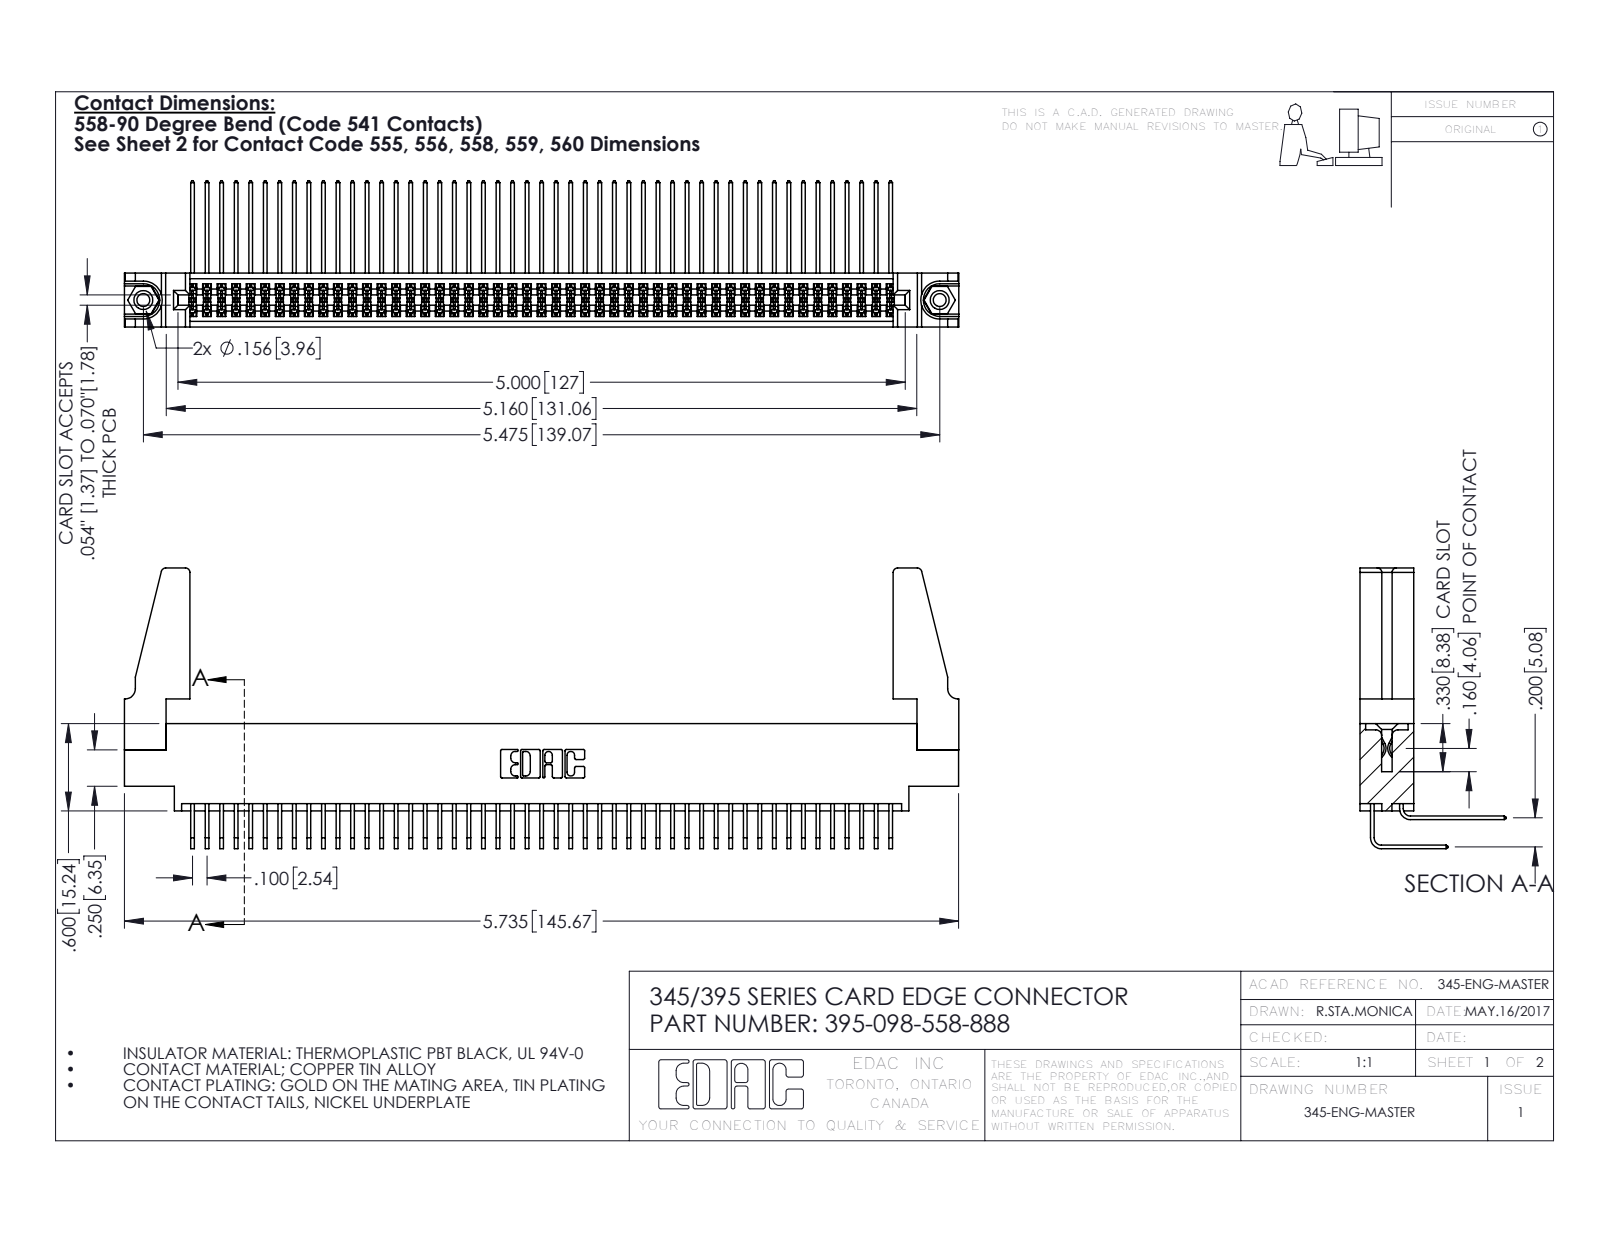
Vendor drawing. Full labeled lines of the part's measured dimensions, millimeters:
Part name (STEP PRODUCT): 345-220-078_345-220-088; 395-098-558-888; 345-250-001_345-250-001-102; 345-292-001_558 559 Tail - 1 (+2 more)
STEP written by: SolidWorks 2016 (CONFIG_CONTROL_DESIGN)
Units: millimetres
Bodies: 103 solids, 5350 faces (3586 planar, 1748 cylindrical, 16 other)
Overall size (bounding box): 145.7 × 49 × 25.5
Volume: 17 930 mm³ · Surface area: 27 740 mm²
Round holes (diameter × count): ⌀2.3 ×2, ⌀3.2 ×2, ⌀4 ×2, ⌀1.6 ×1
Round bosses / shafts (diameter × count): ⌀3.9 ×2
Partial cylindrical surfaces — rounded edges, fillets, slot ends (radius × count): R0.2 ×148, R0.3 ×22, R0.8 ×8, R0.2 ×6, R0.8 ×6, R0.7 ×3, R0.4 ×2, R0.5 ×2
Main face-to-face distances: 1.8, 7.6, 9.4, 5.1, 2.5, 6.9, 0.6, 5.7, 4.4, 0.6
Hole centre spacings: 6.9, 133.1, 139.1
